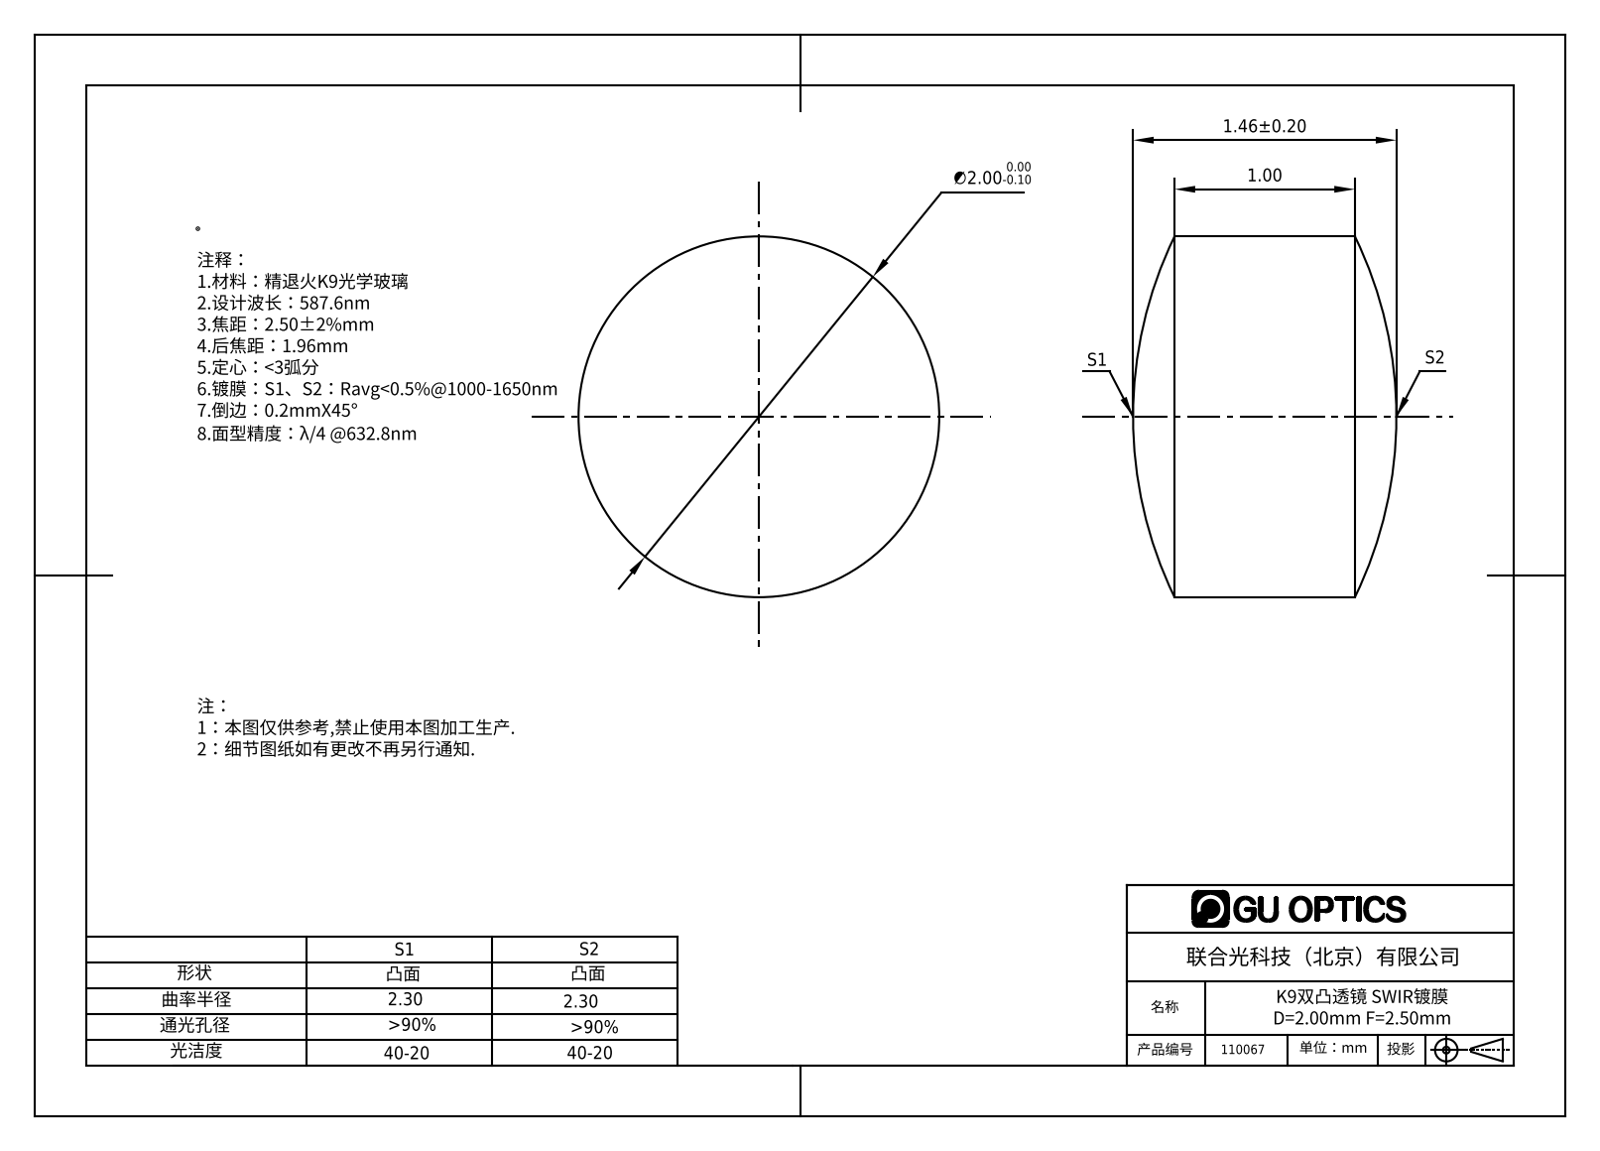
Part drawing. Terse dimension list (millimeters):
name: 110001
written by: SolidWorks 2016 (CONFIG_CONTROL_DESIGN)
unit: mm
bodies: 1 solid, 6 faces (0 planar, 2 cylindrical, 4 other)
size: 2 × 2 × 1.46
volume: 4 mm³; area: 13 mm²
bosses: 1× ⌀2
